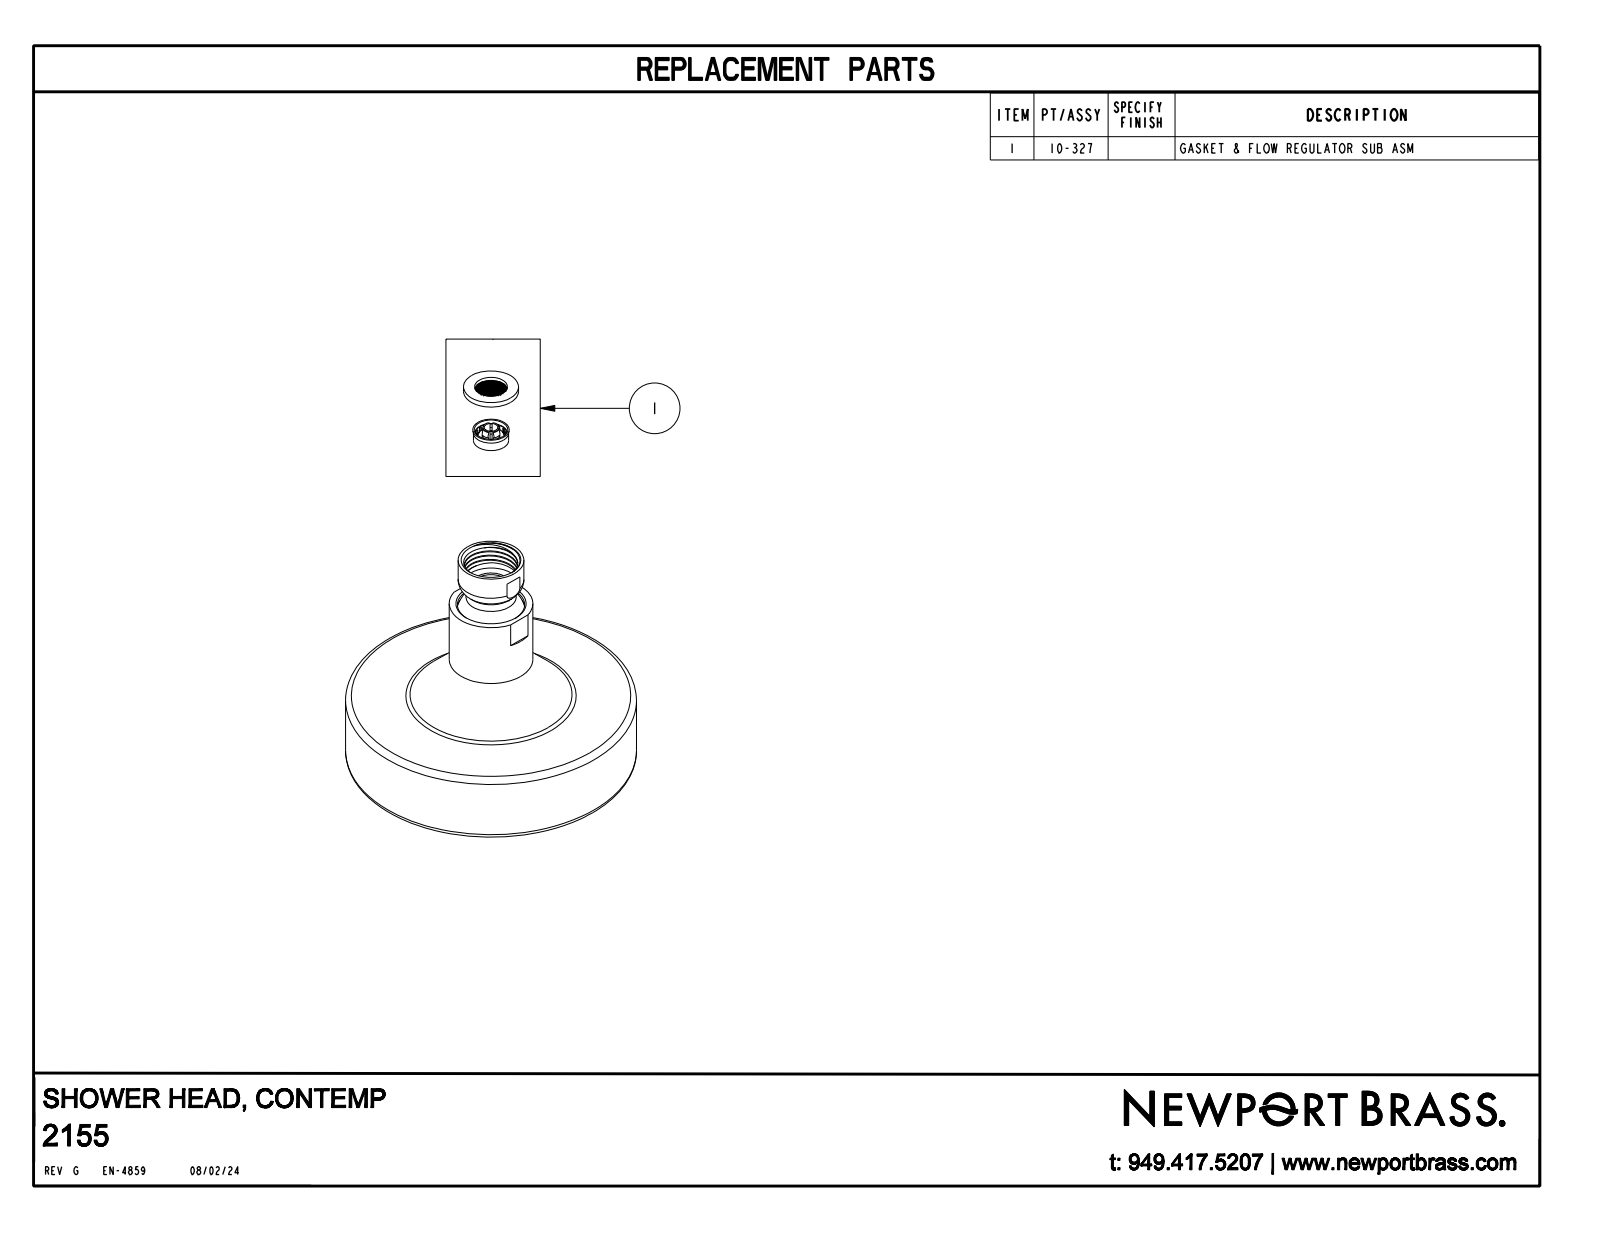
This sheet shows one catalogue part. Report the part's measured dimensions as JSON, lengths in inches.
{"part_name": "11375; 8-083; 12113; 80018 (+1 more)", "step_written_by": "CREO PARAMETRIC BY PTC INC, 2018400 (AUTOMOTIVE_DESIGN)", "units": "inches", "bodies": {"solids": 29, "faces": 3735, "planar": 843, "cylindrical": 1055, "other": 1837}, "overall_size": [4, 4, 3.634], "volume_in3": 22.67, "surface_area_in2": 237.9, "round_holes": [[0.043, 32], [0.098, 15], [0.059, 12], [0.079, 8], [0.096, 8], [0.118, 7], [0.15, 3], [0.252, 3], [0.276, 3], [0.268, 2], [0.394, 2], [0.13, 1]], "round_bosses_or_shafts": [[0.142, 39], [0.165, 23], [0.315, 3], [0.244, 3], [0.228, 2], [4, 1], [3.724, 1], [3.677, 1]], "partial_cylinders_radius": [[0.02, 52], [0.012, 27], [0.083, 15], [0.079, 8], [0.087, 8], [0.743, 5], [0.791, 5], [0.039, 4]], "face_to_face_distances": [0.098, 0.209, 0.289, 0.287, 0.307, 0.987, 0.699, 0.497, 0.49, 0.189], "hole_center_spacings": [0.698, 0.172, 0.322, 0.378, 0.421, 0.437, 0.596, 0.659]}
